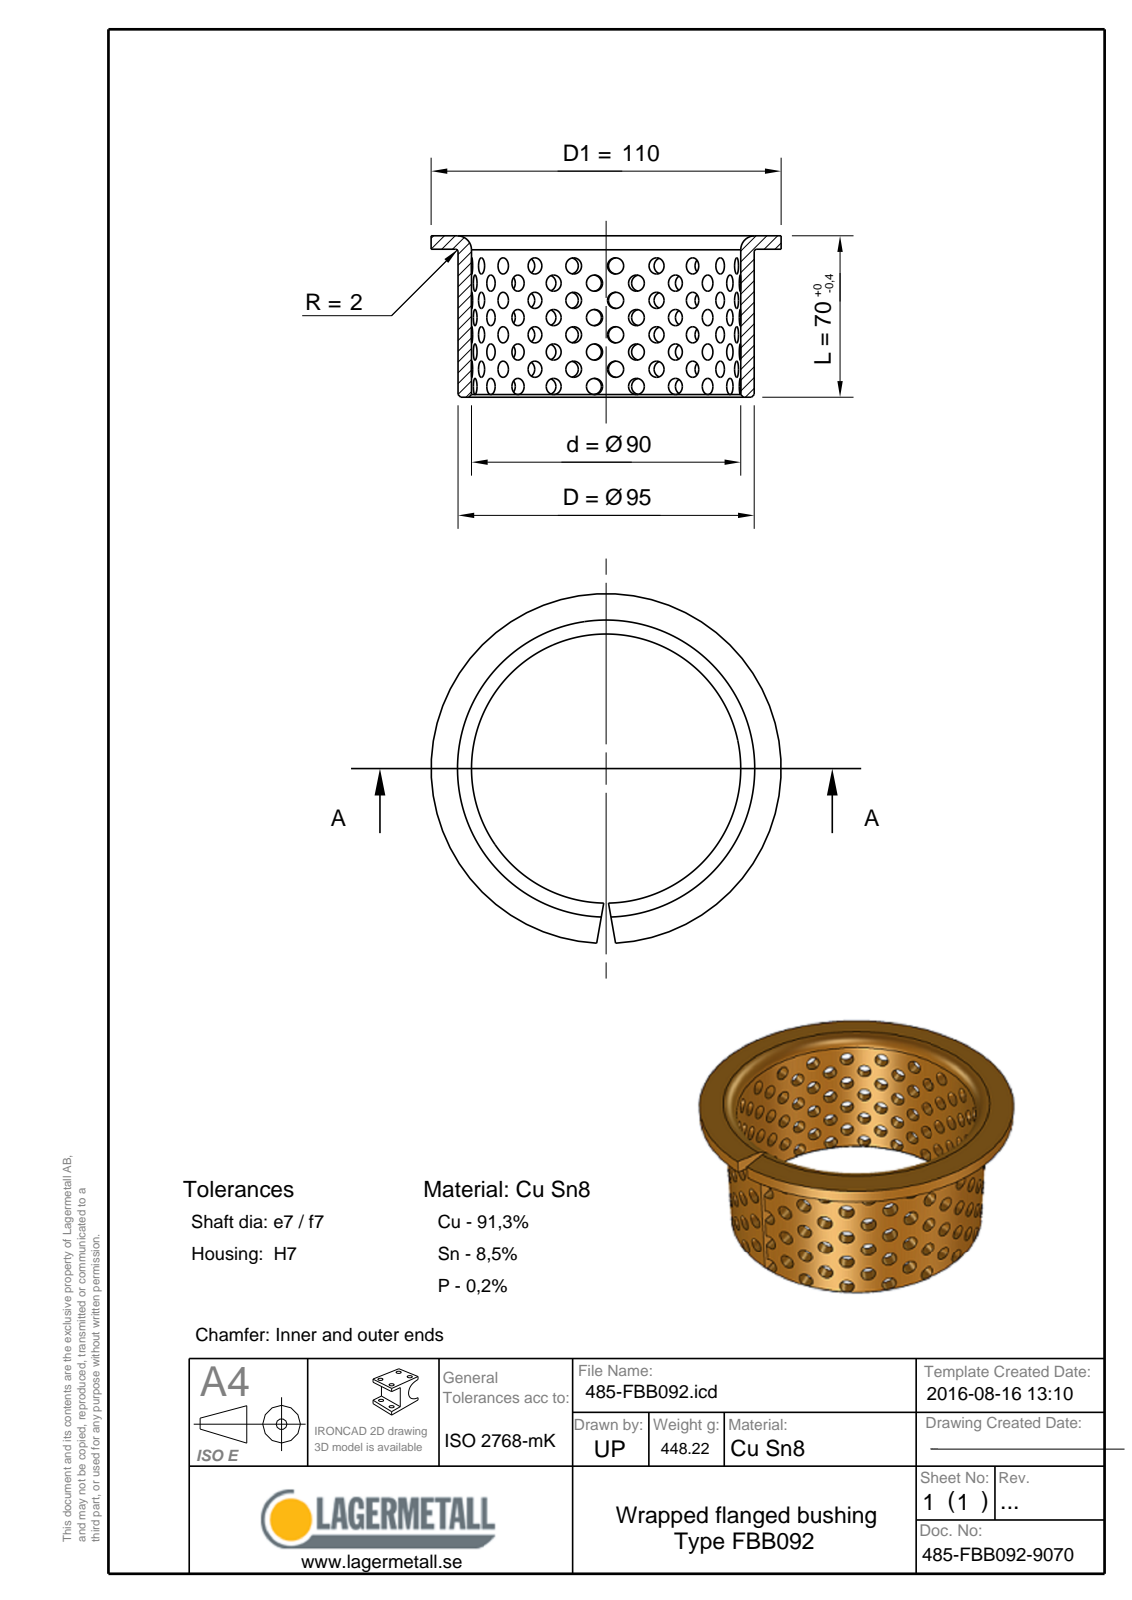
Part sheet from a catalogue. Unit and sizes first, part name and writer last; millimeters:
Units: millimetres
Overall size (bounding box): 110 × 109.96 × 70
Round holes (diameter × count): ⌀90 ×1
Round bosses / shafts (diameter × count): ⌀110 ×1, ⌀95 ×1
Main face-to-face distances: 2.5, 67.5, 70
Volume: 55 336 mm³ · Surface area: 46 140 mm²
Bodies: 1 solid, 12 faces (5 planar, 3 cylindrical, 4 other)
Part name (STEP PRODUCT): 485-FBB092-9070
STEP written by: Spatial InterOp 3D (CONFIG_CONTROL_DESIGN)
